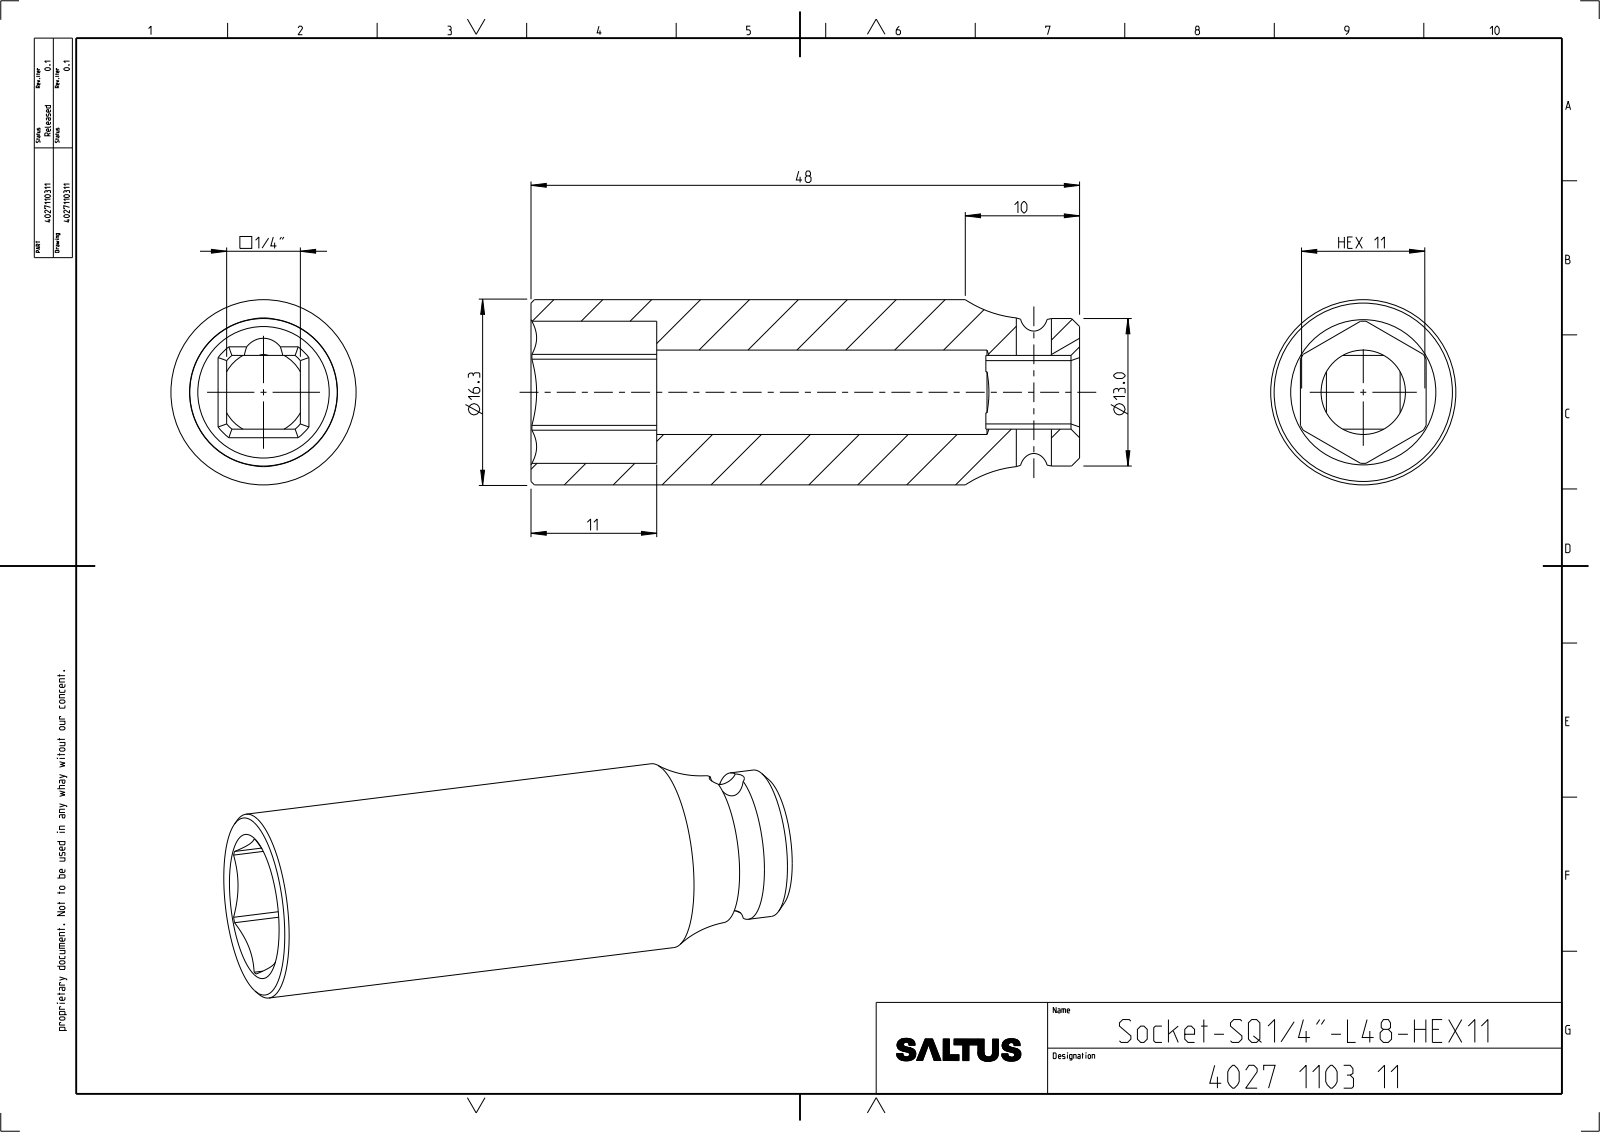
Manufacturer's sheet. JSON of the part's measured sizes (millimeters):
{"part_name": "4027110311", "step_written_by": "CREO PARAMETRIC BY PTC INC, 2022414 (CONFIG_CONTROL_DESIGN)", "units": "millimeters", "bodies": {"solids": 1, "faces": 61, "planar": 22, "cylindrical": 21, "other": 18}, "overall_size": [48, 16.2, 16.2], "volume_mm3": 6422, "surface_area_mm2": 3913, "round_holes": [[3.07, 1], [7.38, 1]], "round_bosses_or_shafts": [[16.2, 1], [12.9, 1]], "partial_cylinders_radius": [[2, 1], [4.25, 1], [6.21, 1]], "face_to_face_distances": [11, 2.27, 8.73, 6.46, 37, 48, 8.2, 28.8, 39.8]}
